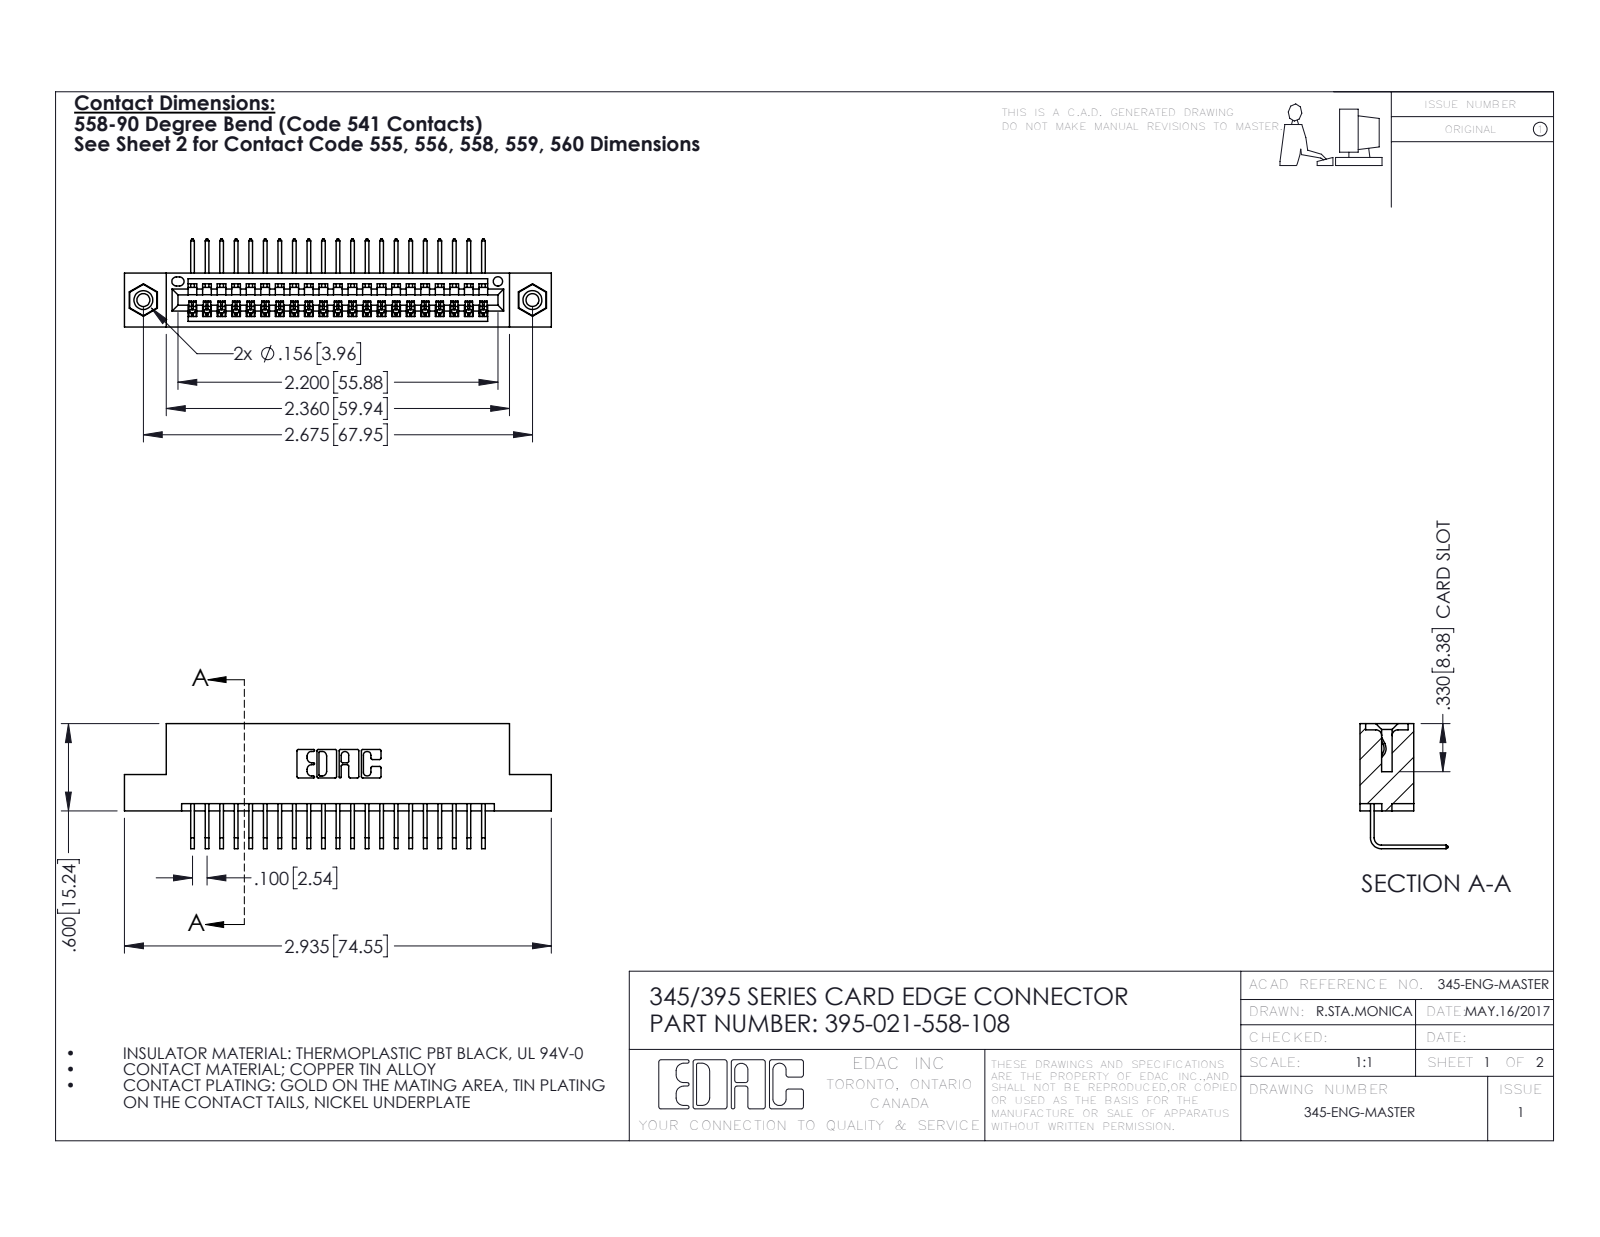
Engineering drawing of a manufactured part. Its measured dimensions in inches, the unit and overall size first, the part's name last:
Units: inches
Overall size (bounding box): 2.935 × 0.859 × 0.605
Round holes (diameter × count): ⌀0.089 ×2, ⌀0.125 ×2, ⌀0.156 ×2, ⌀0.064 ×1
Round bosses / shafts (diameter × count): ⌀0.155 ×2
Partial cylindrical surfaces — rounded edges, fillets, slot ends (radius × count): R0.006 ×42, R0.01 ×22, R0.007 ×6, R0.031 ×6, R0.026 ×3, R0.031 ×2, R0.04 ×2, R0.014 ×1
Main face-to-face distances: 0.072, 0.298, 0.2, 0.37, 0.098, 0.272, 0.025, 0.225, 0.149, 0.072
Hole centre spacings: 0.27, 2.441, 2.675
Volume: 0.425 in³ · Surface area: 14.59 in²
Bodies: 24 solids, 1446 faces (994 planar, 436 cylindrical, 16 other)
Part name (STEP PRODUCT): 345-292-001_558 Tail - 2; 395-021-558-108; 345-250-001_345-250-003-102; 345 Part_Flush Mounting Lugs - 0.156 Dia-TI
STEP written by: SolidWorks 2016 (CONFIG_CONTROL_DESIGN)
